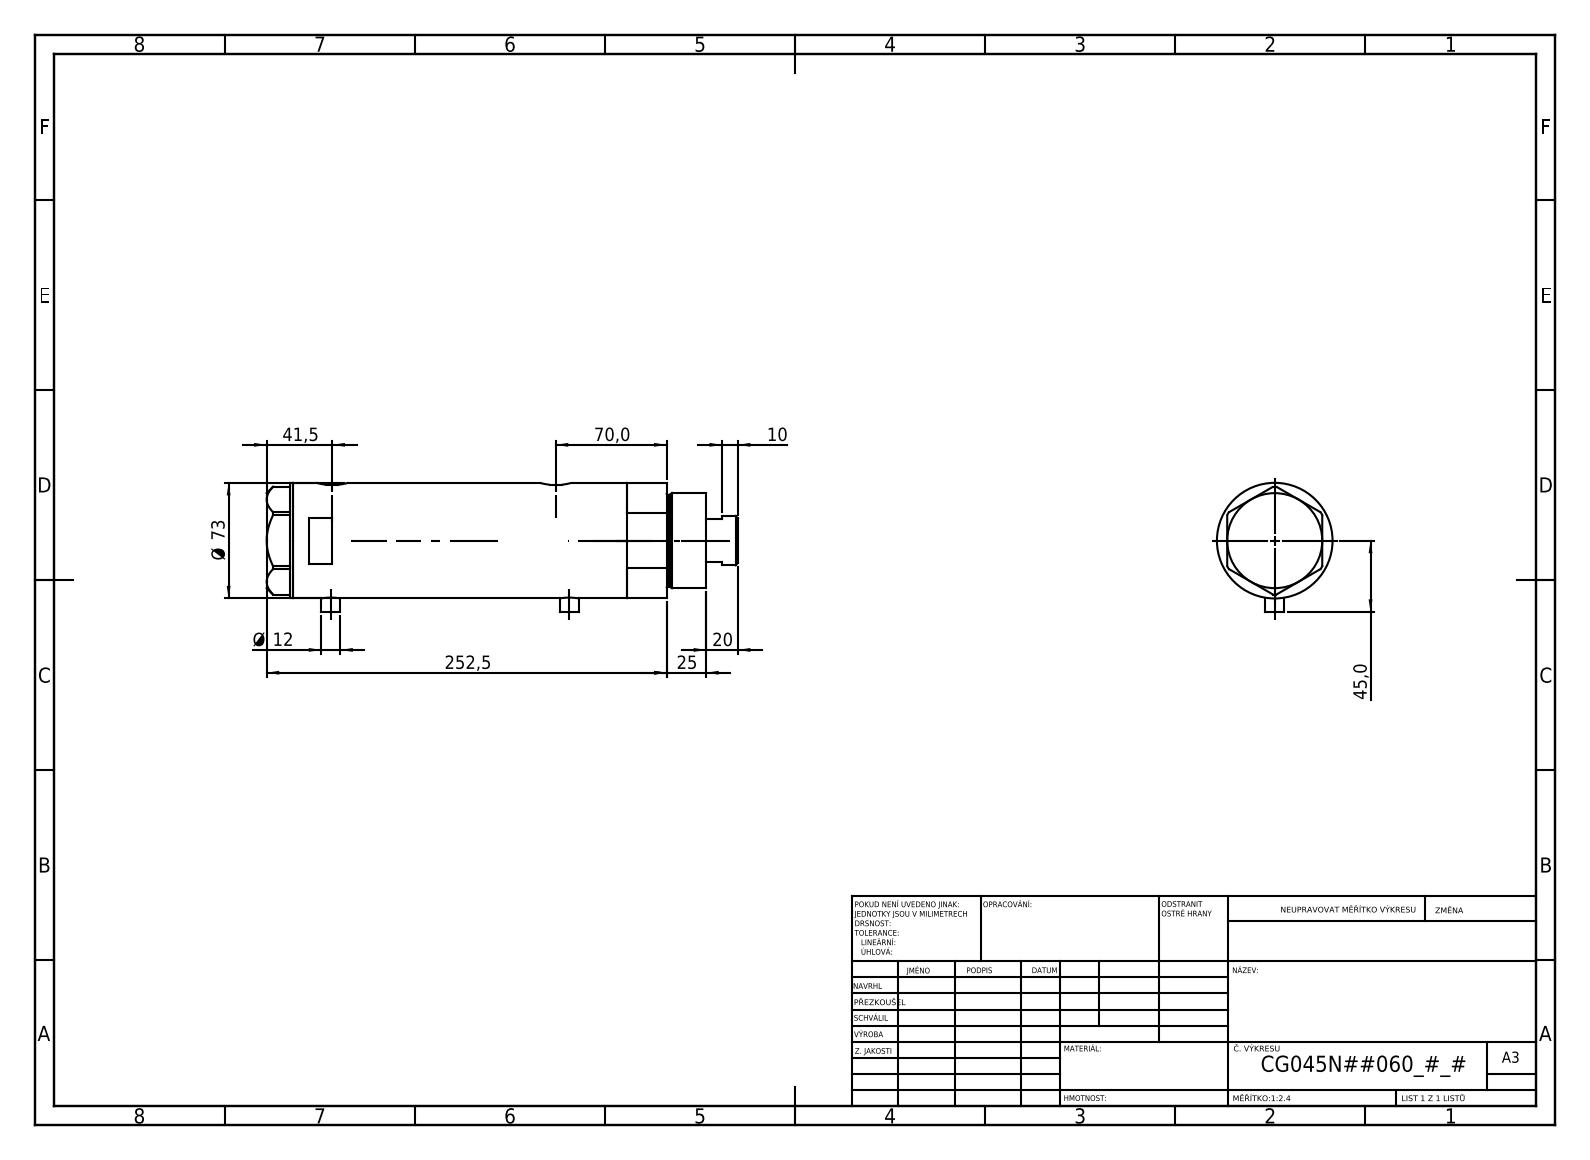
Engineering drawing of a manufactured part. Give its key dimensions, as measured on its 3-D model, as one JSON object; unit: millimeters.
{"part_name": "V270CG_BACK; V270CG_MIDDLE; V270CG_FRONT; V270CG_VC", "step_written_by": "SolidWorks 2019 (CONFIG_CONTROL_DESIGN)", "units": "millimeters", "bodies": {"solids": 4, "faces": 120, "planar": 49, "cylindrical": 51, "other": 20}, "overall_size": [297.5, 81.5, 73], "volume_mm3": 1067000, "surface_area_mm2": 171586, "round_holes": [[12.5, 2], [13.16, 2], [10.5, 1], [32, 1], [33.5, 1], [45, 1], [48, 1], [64, 1]], "round_bosses_or_shafts": [[12, 2], [73, 1], [60, 1], [58, 1], [31, 1]], "partial_cylinders_radius": [[10, 2]], "face_to_face_distances": [166, 26, 140, 16.5, 42.5, 182.5, 60, 2, 261, 277.5], "hole_center_spacings": [1, 8.5, 141, 142, 149.5, 150.5]}
